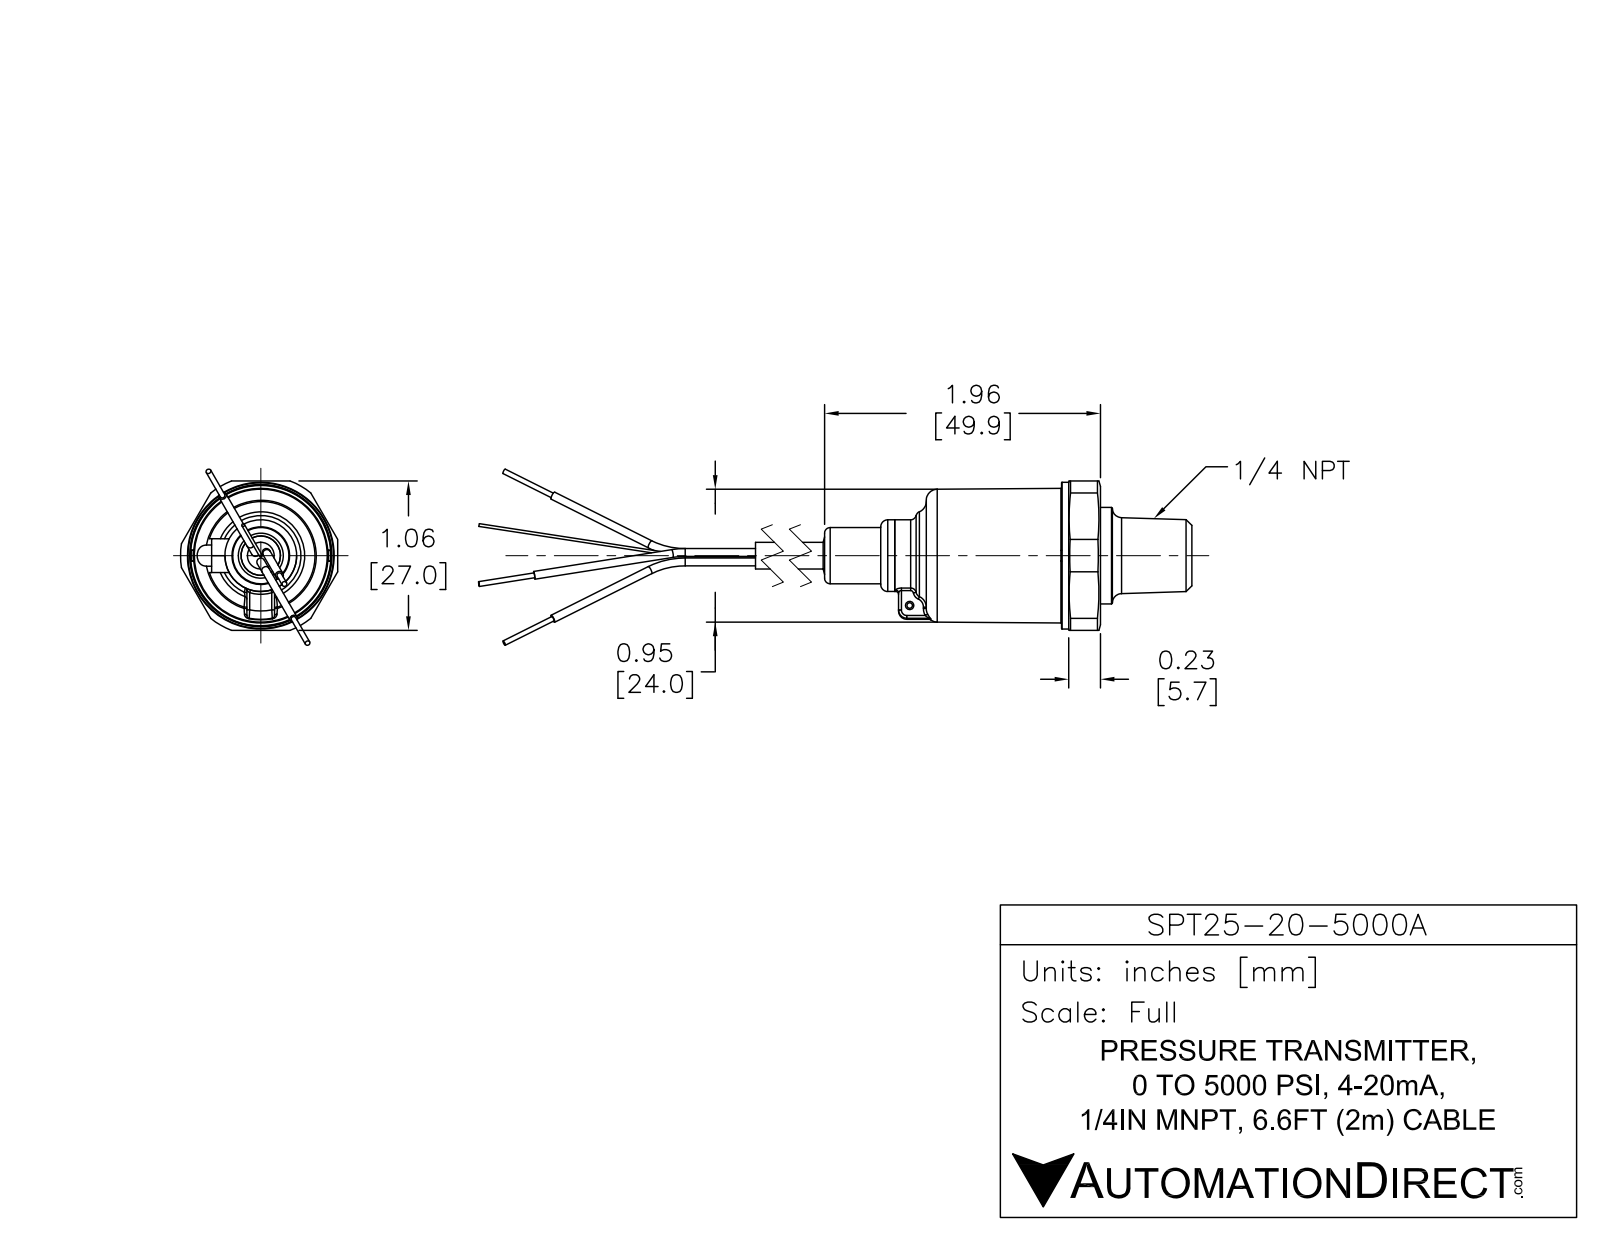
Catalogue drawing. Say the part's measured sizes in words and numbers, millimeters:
The part is named "SPT25-20-5000A". Its 3-D file was written by "SolidWorks 2017 (AUTOMOTIVE_DESIGN)". It is 7 solids with 116 faces: 32 planar, 49 cylindrical and 35 other. Overall it measures 153.3 by 29 by 27.09 millimeters. Its volume is 20 801 cubic millimeters and its surface area 7 170 square millimeters. Round holes: 1 of diameter 1, 1 of diameter 3.3. Round bosses or shafts: 6 of diameter 1.4, 5 of diameter 0.75, 1 of diameter 26.75, 1 of diameter 24, 1 of diameter 17.5, 1 of diameter 14, 1 of diameter 13, 1 of diameter 10. Partial cylindrical surfaces (rounded edges, fillets, slot ends): 1 of radius 2, 1 of radius 14.5. The main face-to-face distances are 6.75, 24, 17.25, 42.75, 49.5, 66.75, 44, 1.25, 5.5, 22.75.
